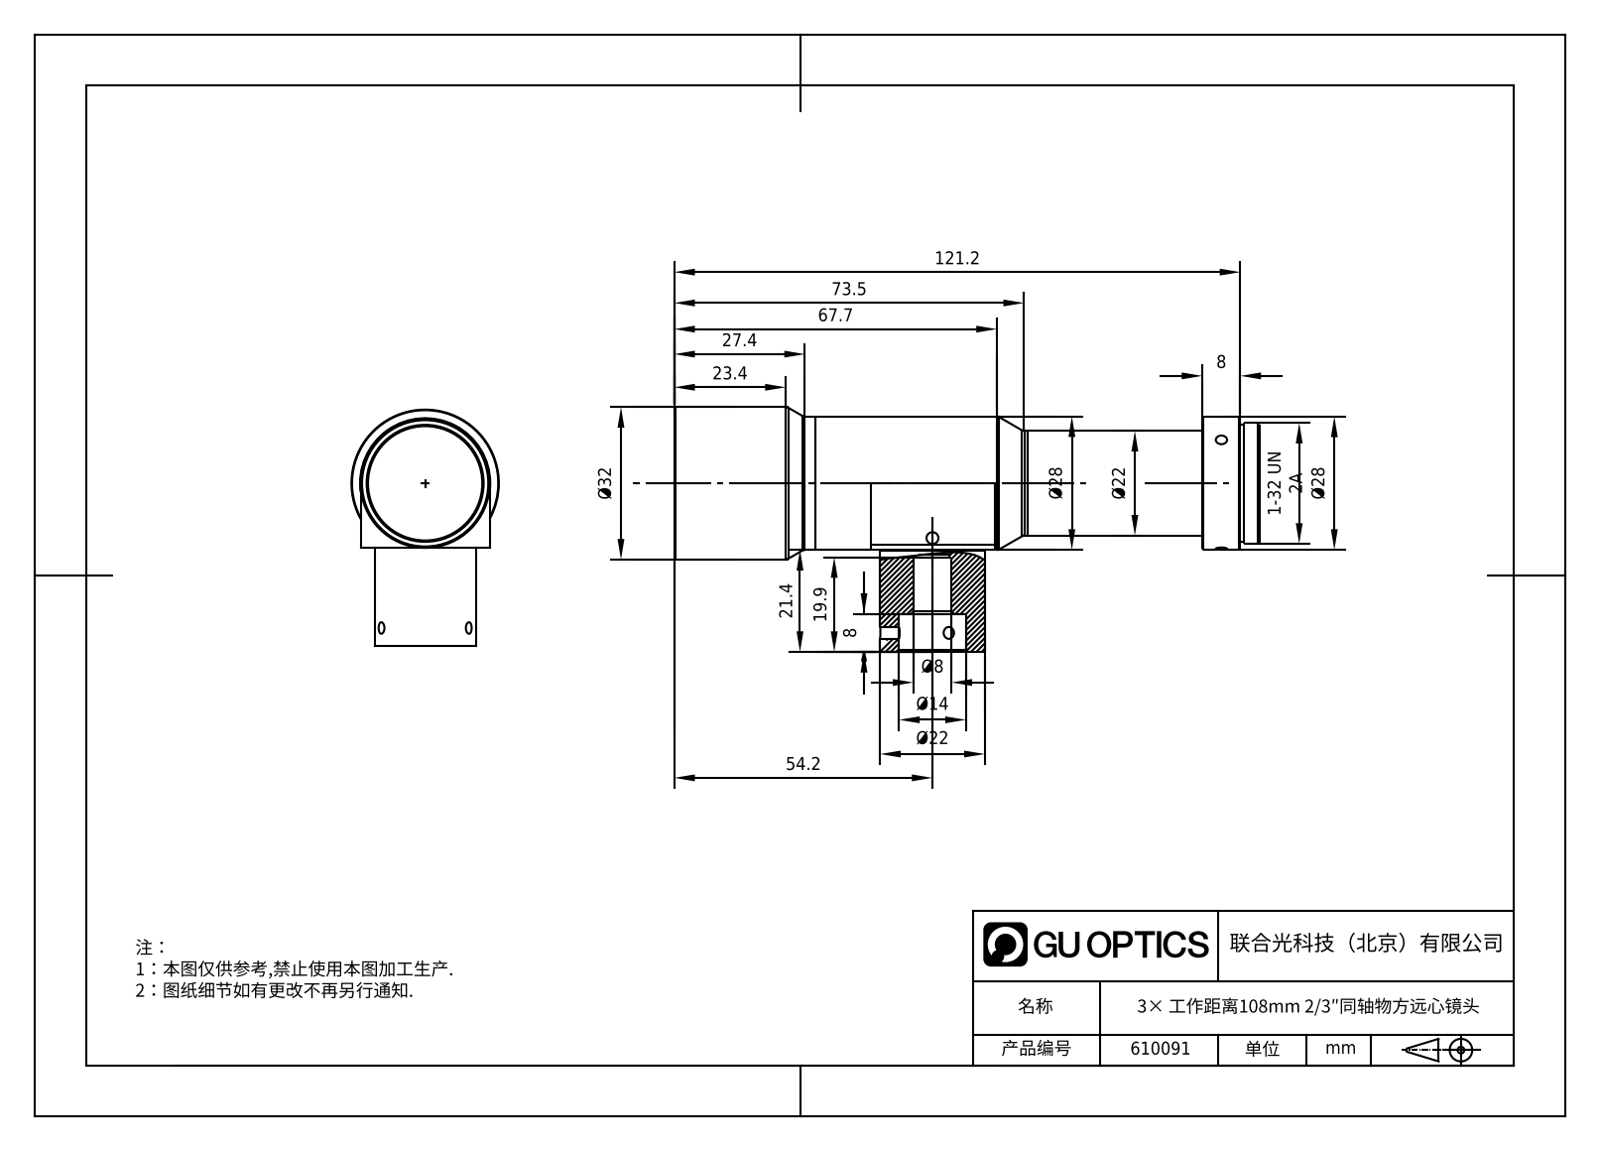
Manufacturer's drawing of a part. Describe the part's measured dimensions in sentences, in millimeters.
The part is named "WWH30-108CTV3". Its 3-D file was written by "SolidWorks 2017 (CONFIG_CONTROL_DESIGN)". It is 1 solid with 48 faces: 13 planar, 15 cylindrical and 20 other. Overall it measures 125.2 by 51.4 by 32 millimeters. Its volume is 81 645 cubic millimeters and its surface area 14 233 square millimeters. Round bosses or shafts: 2 of diameter 22, 1 of diameter 32, 1 of diameter 28, 1 of diameter 25.4, 1 of diameter 24.4. The main face-to-face distances are 125.2, 28, 21.4, 113.2, 12, 121.2, 8, 4, 67.2, 46.
